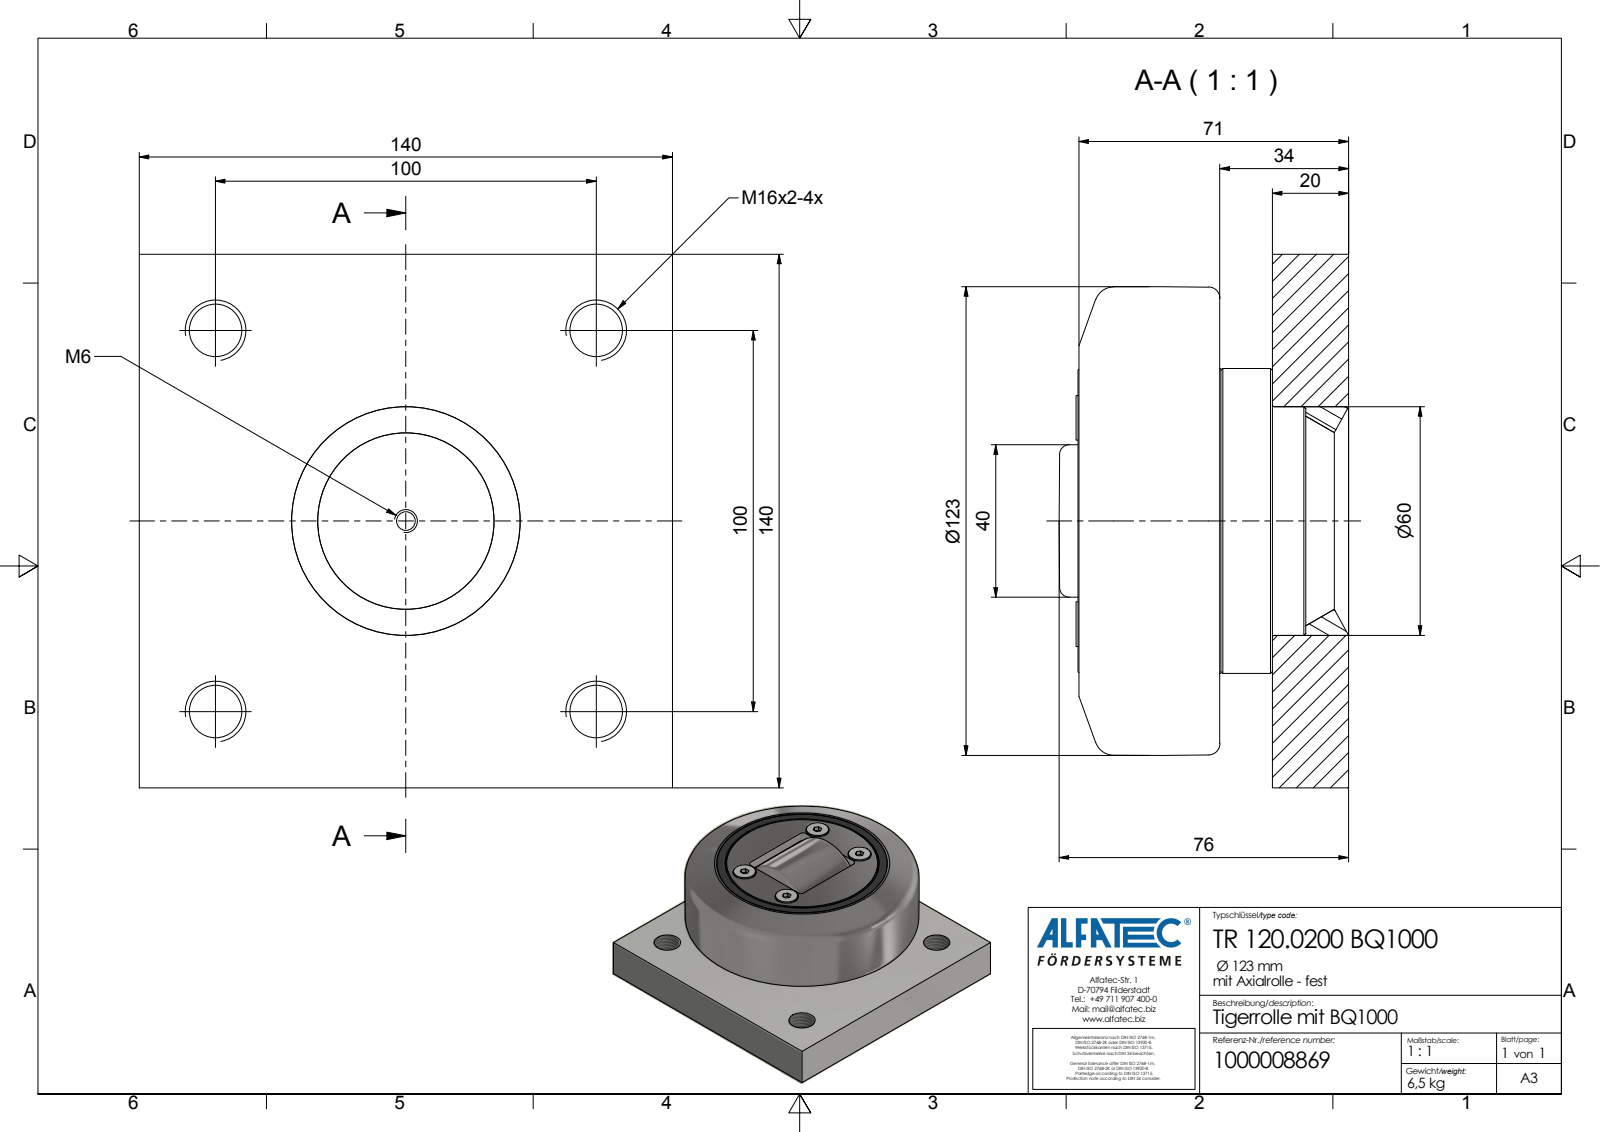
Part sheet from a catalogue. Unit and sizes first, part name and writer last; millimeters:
Units: millimetres
Overall size (bounding box): 140 × 140 × 76
Round holes (diameter × count): ⌀3 ×4, ⌀13.84 ×4, ⌀4.92 ×1, ⌀22.3 ×1, ⌀29.3 ×1, ⌀33.5 ×1, ⌀71 ×1, ⌀81 ×1, ⌀87 ×1, ⌀89.5 ×1, ⌀95 ×1
Round bosses / shafts (diameter × count): ⌀11.7 ×4, ⌀84.5 ×1, ⌀80 ×1, ⌀79.8 ×1, ⌀79 ×1, ⌀69.5 ×1
Partial cylindrical surfaces — rounded edges, fillets, slot ends (radius × count): R2 ×8, R1.5 ×2, R24.5 ×1
Main face-to-face distances: 20, 140, 33.8, 13.8, 6.5, 71, 51, 37.2, 30.5, 30.7
Hole centre spacings: 70.71, 100, 141.42
Volume: 778 382 mm³ · Surface area: 130 626 mm²
Bodies: 3 solids, 143 faces (68 planar, 48 cylindrical, 27 other)
Part name (STEP PRODUCT): TR 120.0200 BQ1000_Kontur
STEP written by: Autodesk Inventor 2020 (AUTOMOTIVE_DESIGN)
